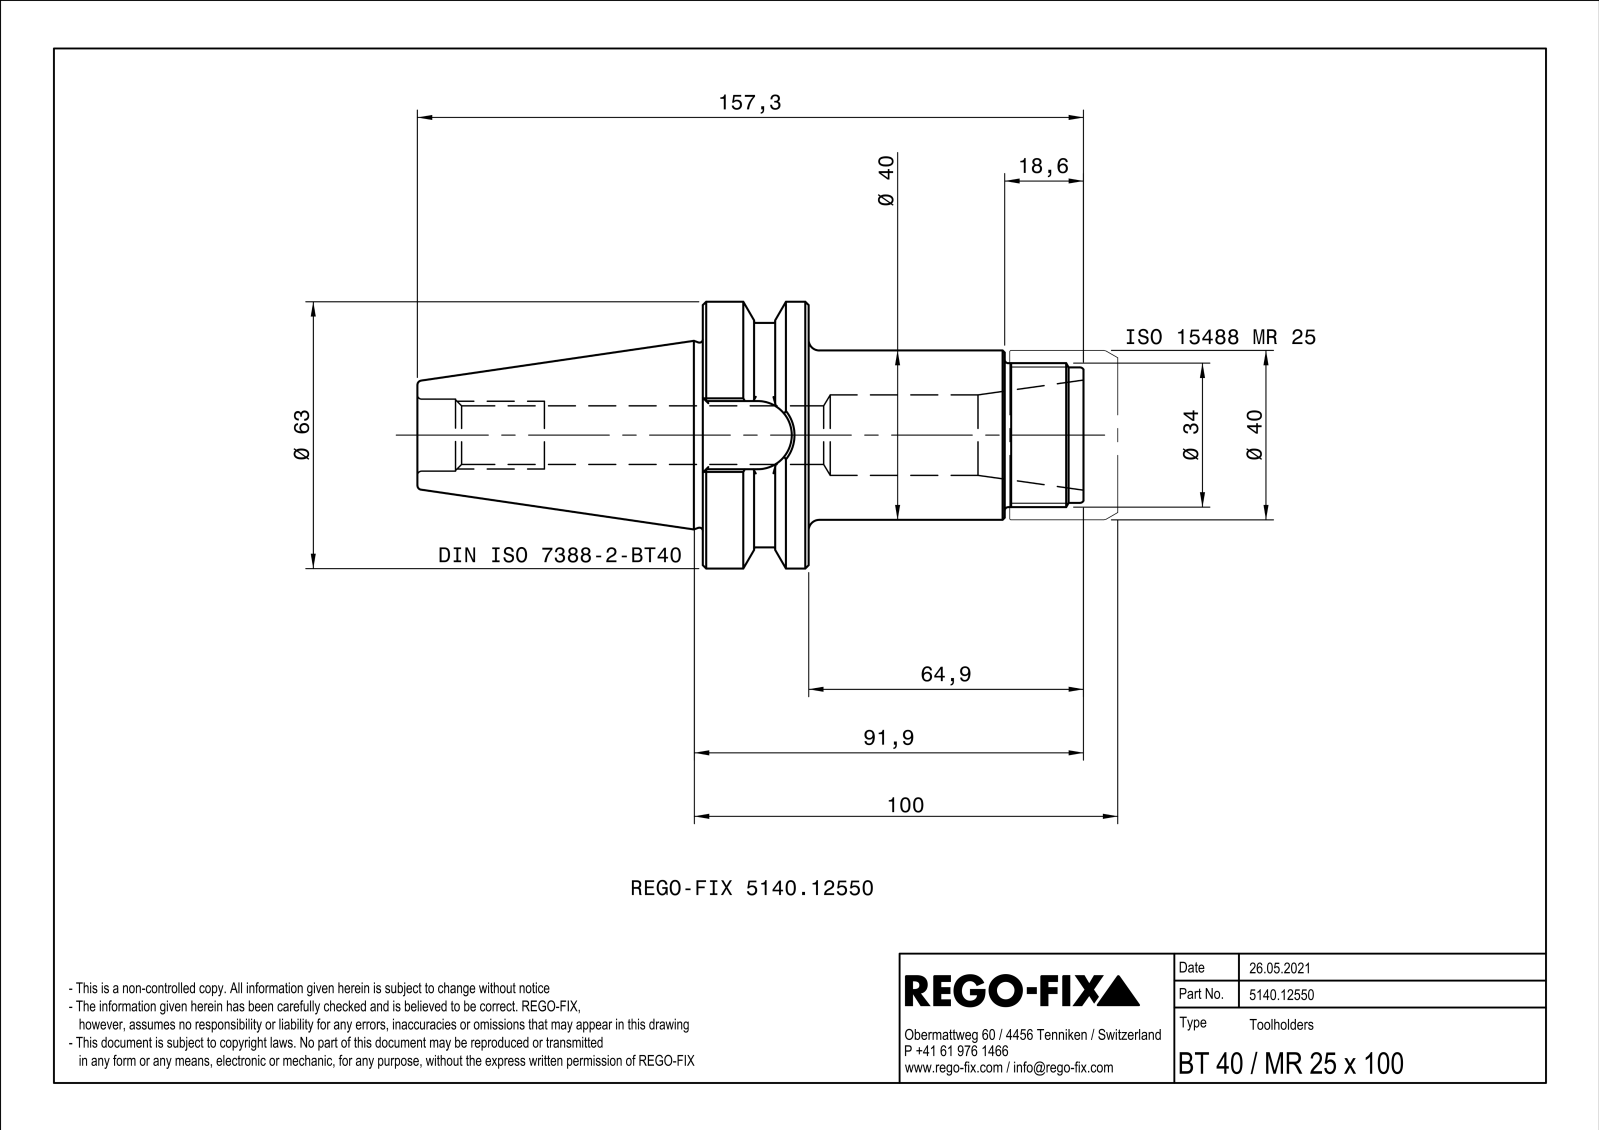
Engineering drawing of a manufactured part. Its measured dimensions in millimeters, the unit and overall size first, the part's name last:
Units: millimetres
Overall size (bounding box): 157.3 × 63 × 63
Round holes (diameter × count): ⌀13.84 ×1, ⌀17 ×1, ⌀19 ×1
Round bosses / shafts (diameter × count): ⌀63 ×1, ⌀53 ×1, ⌀40 ×1, ⌀34 ×1, ⌀32 ×1
Partial cylindrical surfaces — rounded edges, fillets, slot ends (radius × count): R0.5 ×4, R8.05 ×1
Main face-to-face distances: 25, 45.1, 46.3, 71.3, 18.6, 64.9, 89.9, 157.3, 138.7, 92.4
Volume: 173 974 mm³ · Surface area: 33 546 mm²
Bodies: 1 solid, 85 faces (37 planar, 19 cylindrical, 29 other)
Part name (STEP PRODUCT): 0007675
STEP written by: SIEMENS PLM Software Solid Edge ST10 (AUTOMOTIVE_DESIGN)
